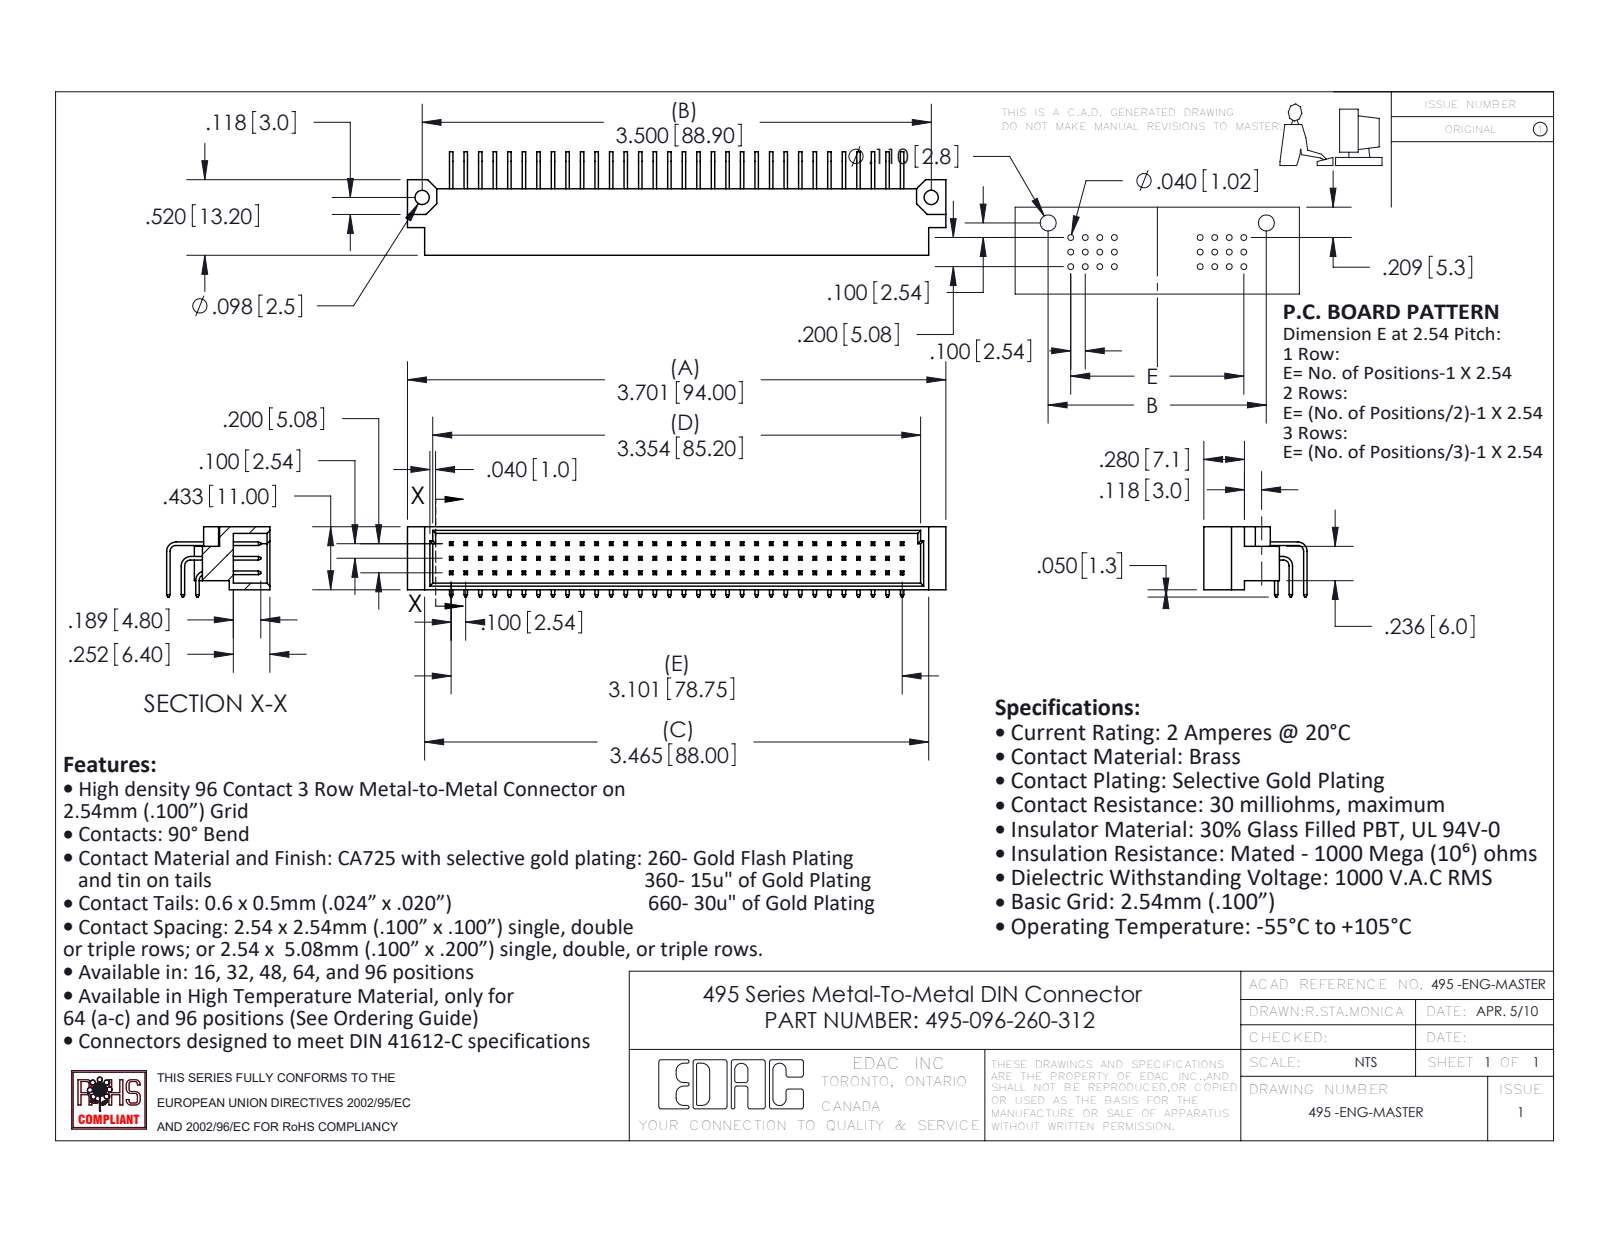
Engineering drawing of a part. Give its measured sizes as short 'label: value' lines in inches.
name: 495-290-3; 495-290-1; 495 Part_96; 495-096-260-312 (+1 more)
written by: SolidWorks 2020 (AUTOMOTIVE_DESIGN)
unit: in
bodies: 97 solids, 2161 faces (1965 planar, 196 cylindrical, 0 other)
size: 3.701 × 0.711 × 0.483
volume: 0.404 in³; area: 17.74 in²
holes: 2× ⌀0.098
rounds: 3× R0.04, 3× R0.065
face distances: 0.1, 0.024, 0.2, 0.205, 0.045, 0.388, 0.124, 0.076, 0.433, 0.343
hole spacings: 3.5
